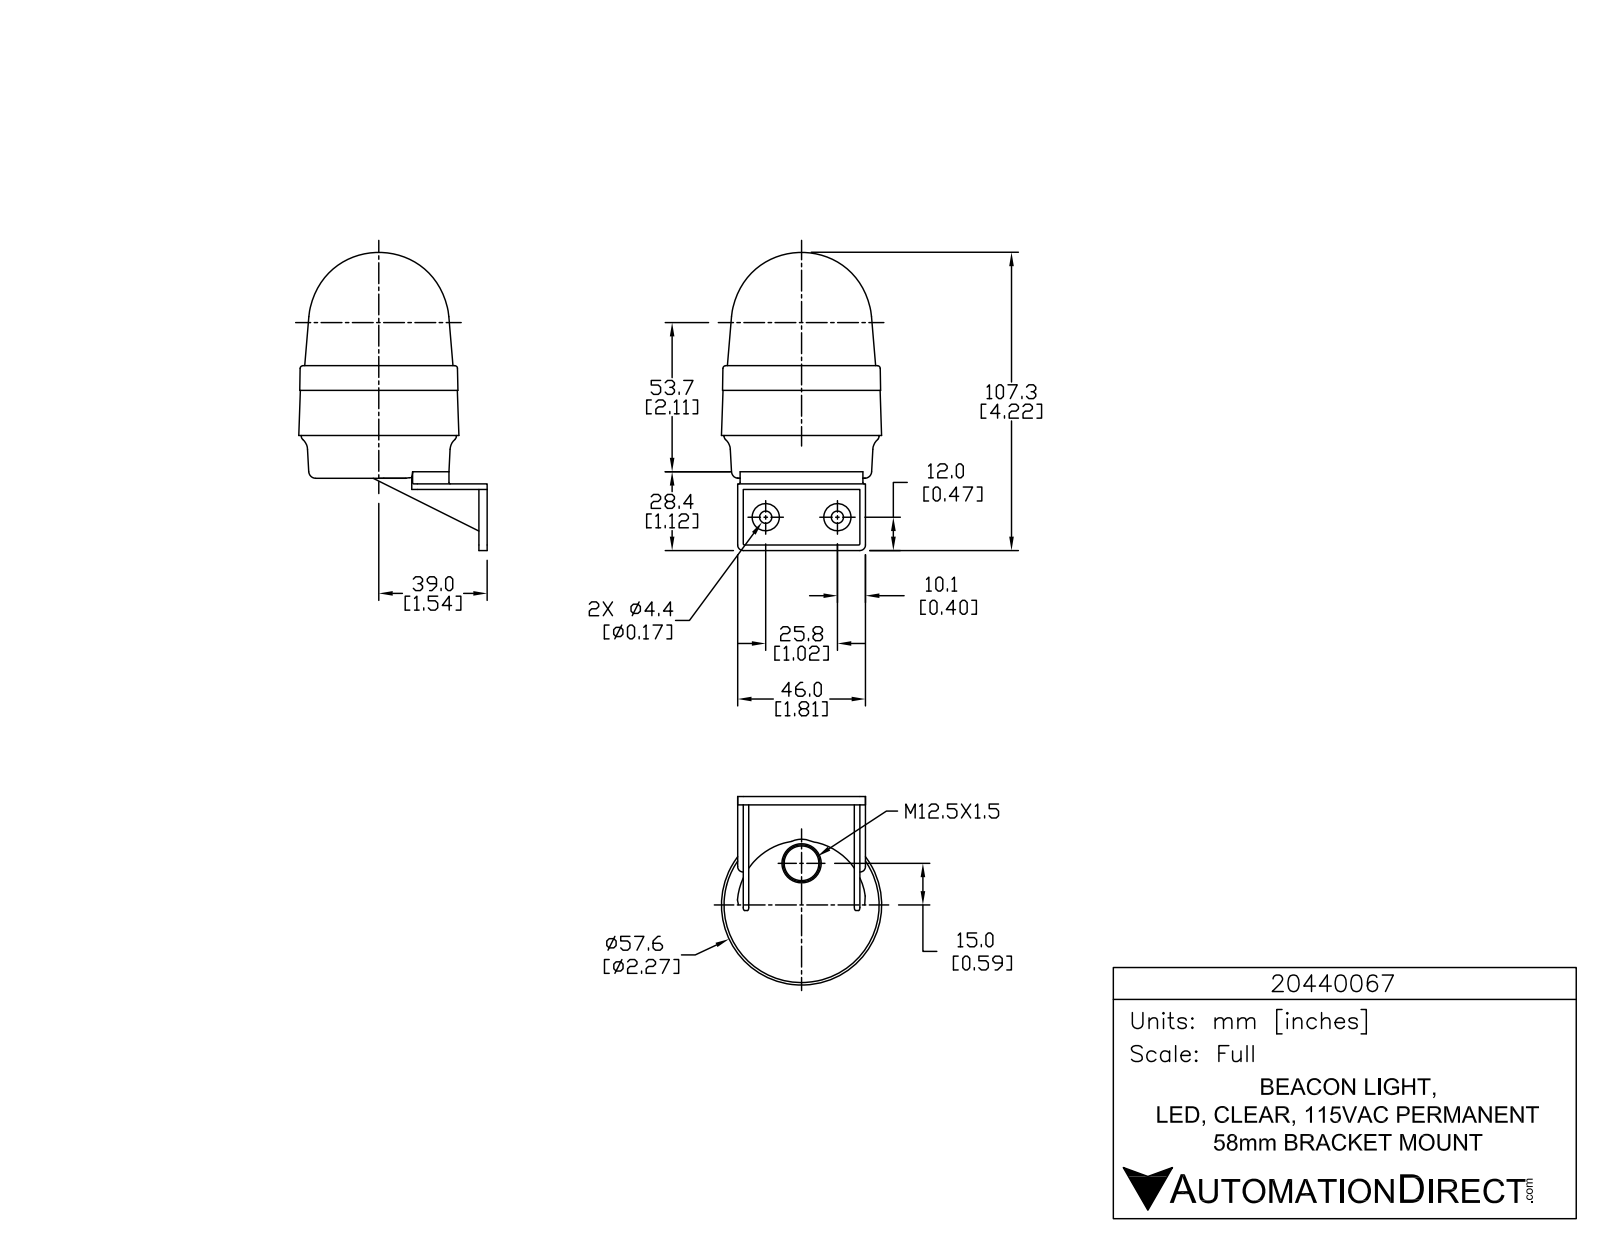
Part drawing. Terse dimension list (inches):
name: 20440067
written by: SolidWorks 2015 (AUTOMOTIVE_DESIGN)
unit: in
bodies: 1 solid, 828 faces (551 planar, 179 cylindrical, 98 other)
size: 4.225 × 2.852 × 2.407
volume: 10.27 in³; area: 33.38 in²
holes: 3× ⌀0.039, 2× ⌀0.173
bosses: 3× ⌀0.226, 3× ⌀0.056, 2× ⌀0.386, 1× ⌀2.197
rounds: 6× R0.008, 6× R0.008, 6× R0.008, 6× R0.02, 6× R0.131, 4× R0.079, 3× R0.004, 3× R0.005
face distances: 0.079, 0.157, 1.575, 1.654, 0.039, 0.118, 1.496, 0.866, 0.945, 0.764
hole spacings: 1.016
